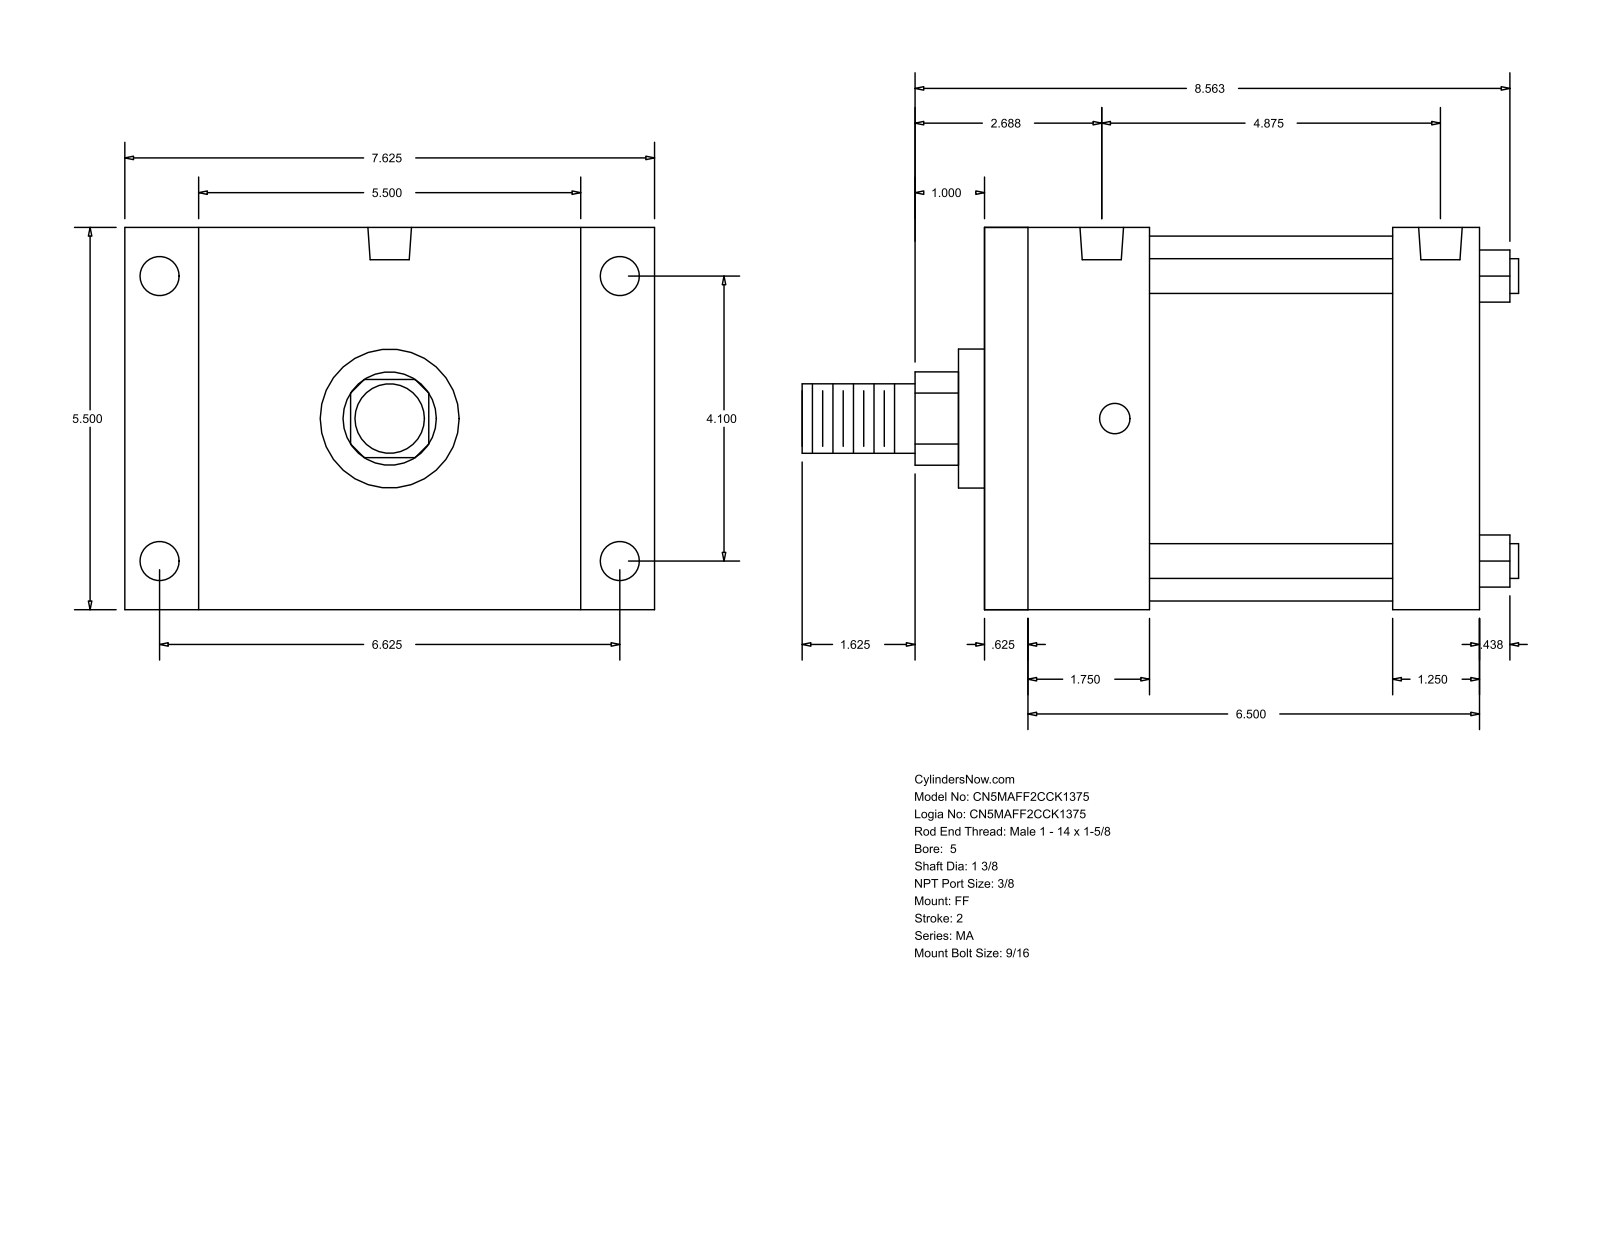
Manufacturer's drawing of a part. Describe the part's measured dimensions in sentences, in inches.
The part is named "MA_FF__0500_1.375". Its 3-D file was written by "GSSL Pune (CONFIG_CONTROL_DESIGN)". It is 0 solids with 92 faces: 64 planar, 28 cylindrical and 0 other. Overall it measures 10.313 by 7.625 by 5.5 inches. Round holes: 4 of diameter 0.437, 4 of diameter 0.563, 2 of diameter 0.627. Round bosses or shafts: 4 of diameter 0.5, 1 of diameter 5.25, 1 of diameter 2, 1 of diameter 1.375, 1 of diameter 1. Partial cylindrical surfaces (rounded edges, fillets, slot ends): 1 of radius 0.672. The main face-to-face distances are 5.5, 7.125, 0.625, 6.5, 5.875, 5.25, 1.25, 2.375, 1.75, 3.5. The hole center spacings are 0.188, 4.1, 4.5, 4.687, 6.625, 7.791, 4.875.
